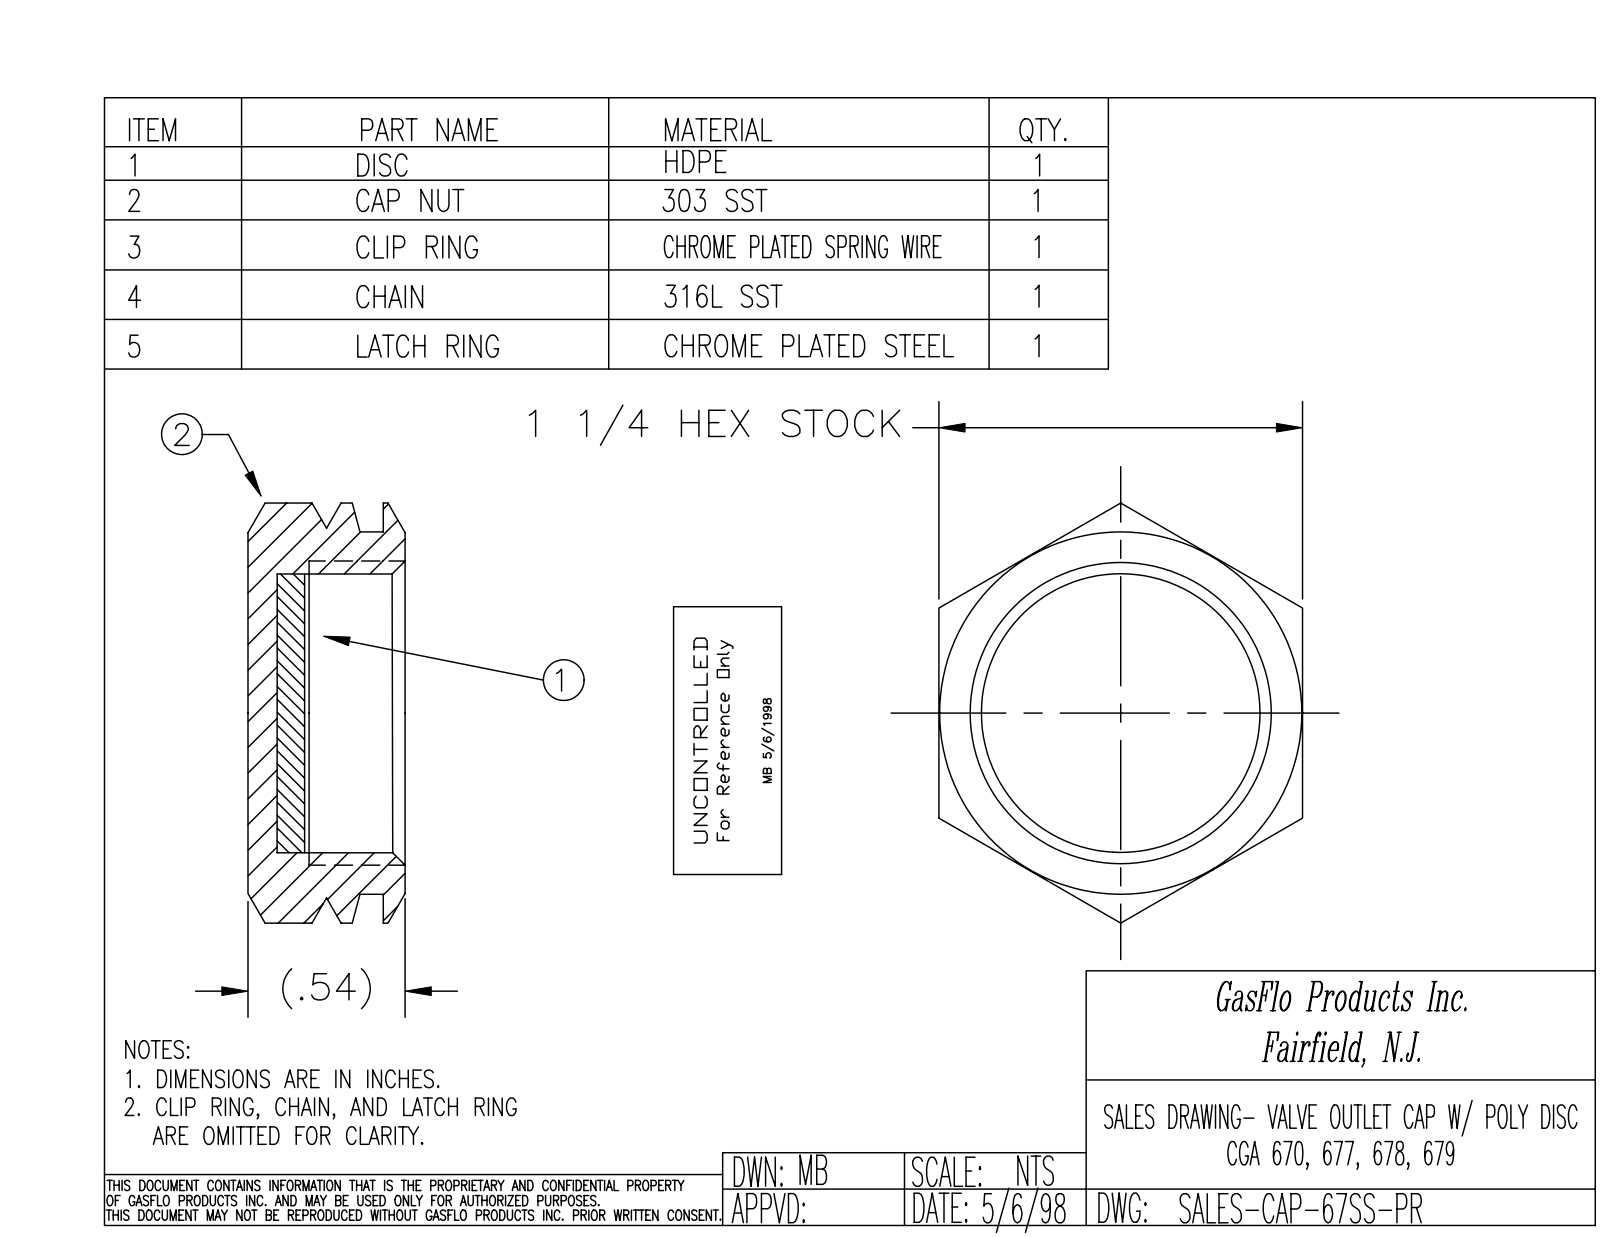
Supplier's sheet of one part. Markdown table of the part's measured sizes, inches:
| quantity | value |
| --- | --- |
| part name | PRT-002255_SMALL PIN; PRT-002239_STAINLESS; ASY-000211_Straight Chain; PRT-004002 (+5 more) |
| STEP written by | SolidWorks 2018 (CONFIG_CONTROL_DESIGN) |
| units | inches |
| bodies | 13 solids, 316 faces (56 planar, 117 cylindrical, 143 other) |
| overall size | 4.139 × 1.965 × 1.555 |
| volume | 0.533 in³ |
| surface area | 13.69 in² |
| round holes (diameter × count) | 0.063 × 1, 0.962 × 1 |
| round bosses / shafts (diameter × count) | 0.063 × 30, 1.243 × 1, 0.963 × 1, 0.1 × 1 |
| partial cylindrical surfaces (radius × count) | 0.005 × 24, 0.25 × 4, 0.01 × 2 |
| main face-to-face distances | 0.1, 1.25, 0.094, 0.194, 0.346, 0.44, 0.54, 0.073, 0.273, 0.367 |
| hole center spacings | 0.478 |
